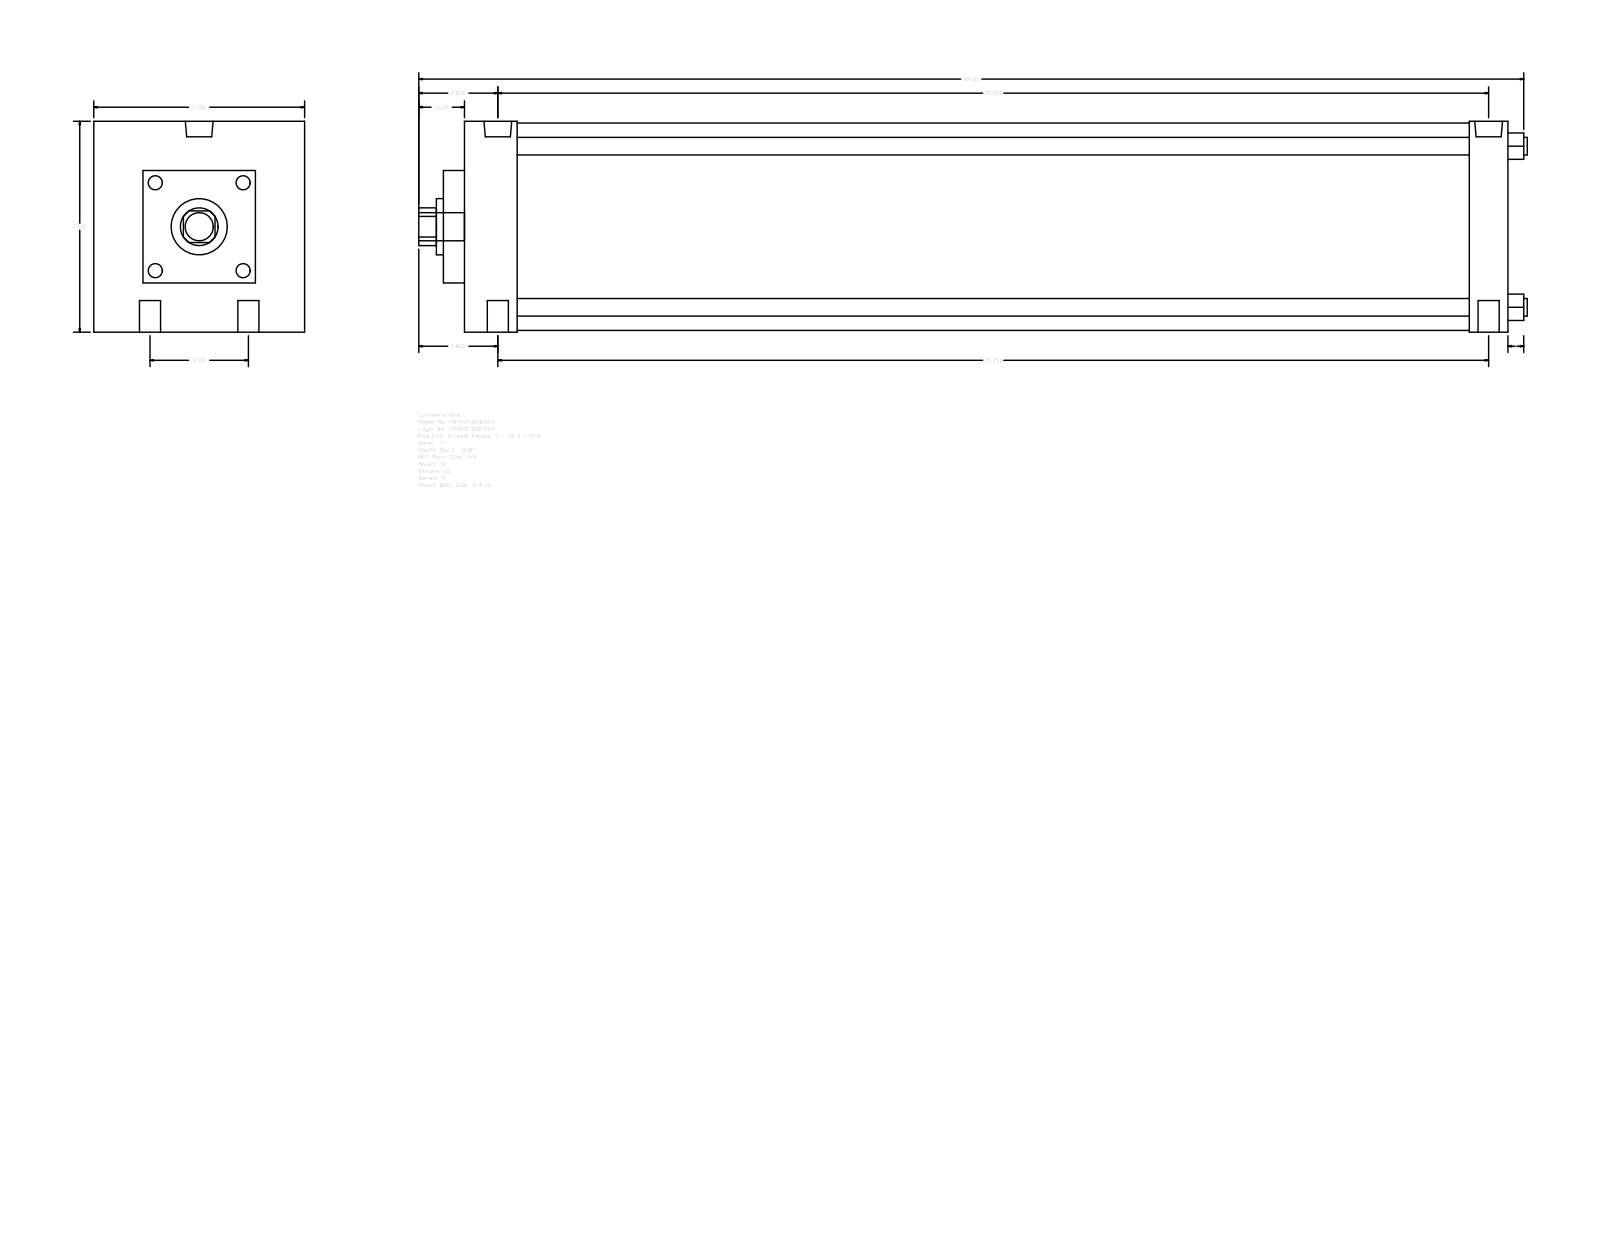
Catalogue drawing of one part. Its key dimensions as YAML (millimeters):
part_name: "A_SF__0700_1.375"
step_written_by: "GSSL Pune (CONFIG_CONTROL_DESIGN)"
units: millimeters
bodies: {solids: 0, faces: 93, planar: 67, cylindrical: 26, other: 0}
overall_size: [1001.71, 190.5, 190.5]
round_holes:
  - {diameter: 19.05, count: 4}
  - {diameter: 15.08, count: 2}
  - {diameter: 25.12, count: 2}
  - {diameter: 34.92, count: 1}
  - {diameter: 50.8, count: 1}
round_bosses_or_shafts:
  - {diameter: 15.88, count: 4}
  - {diameter: 187.32, count: 1}
  - {diameter: 25.4, count: 1}
partial_cylinders:
  - {radius: 17.06, count: 1}
face_to_face_distances: [190.5, 942.98, 19.04, 962.02, 66.67, 927.1, 47.63, 908.06, 860.43, 895.35]
hole_center_spacings: [44.45, 896.45, 895.35, 88.9, 899.75, 884.23]
